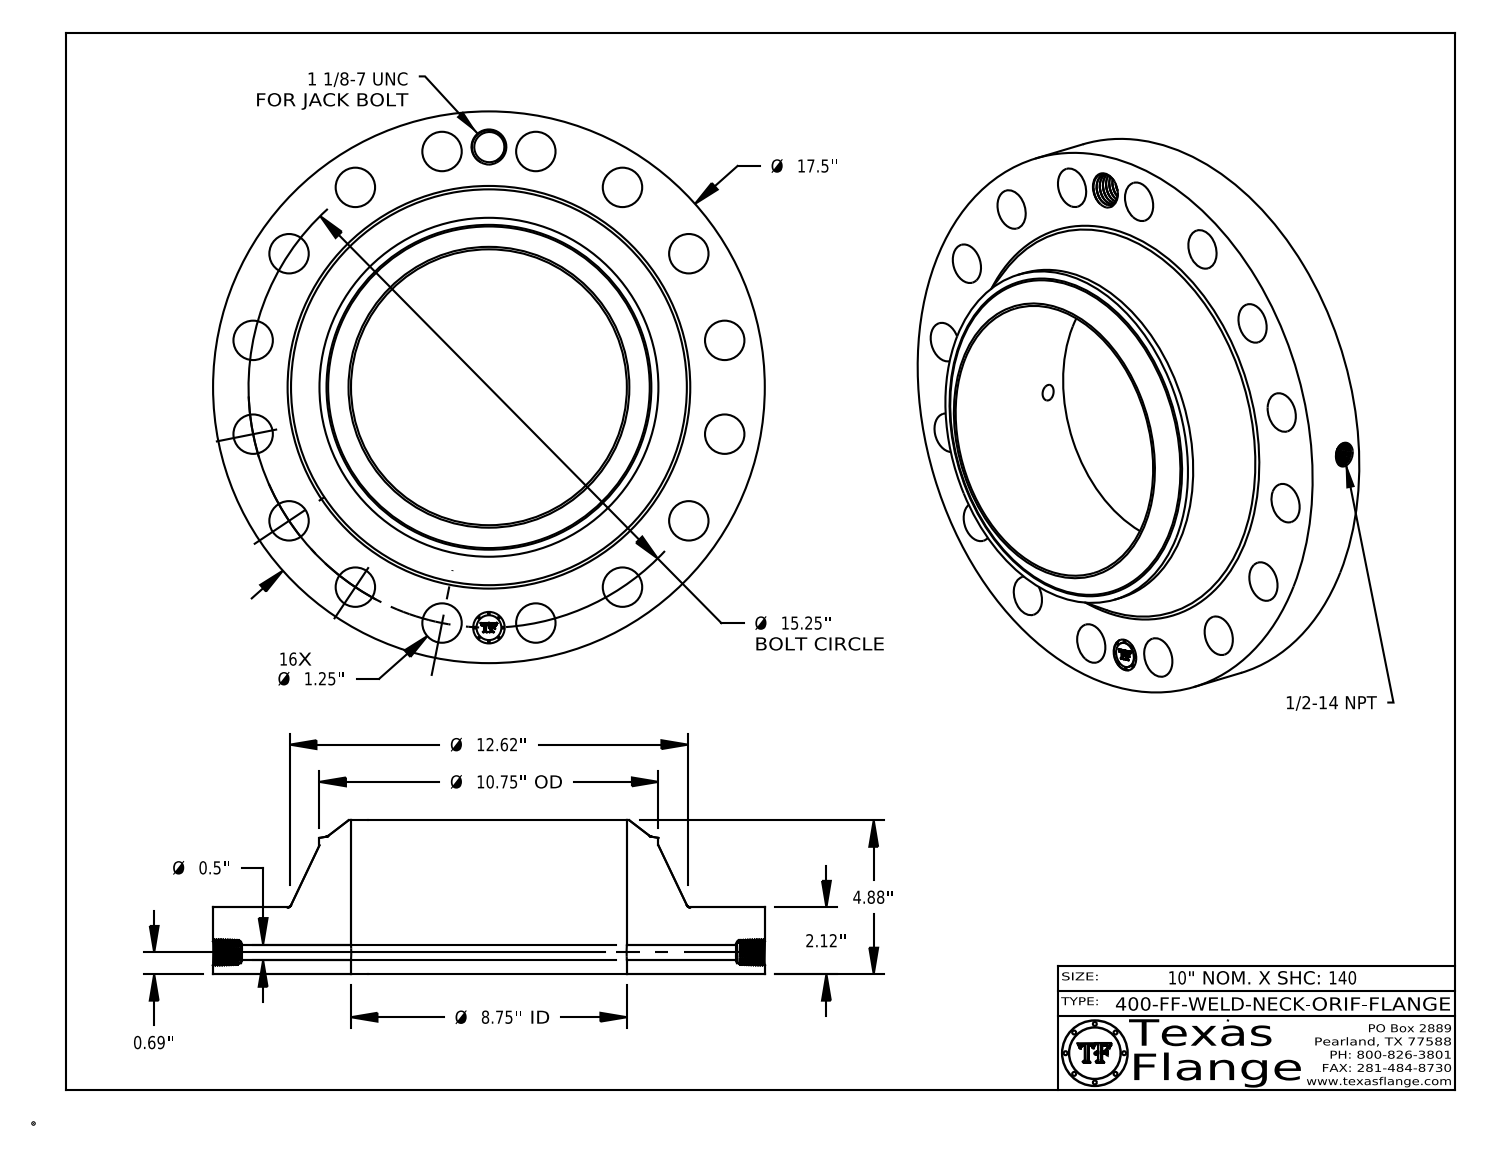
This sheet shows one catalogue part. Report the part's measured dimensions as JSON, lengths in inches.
{"part_name": "400-FF-WELD-NECK", "step_written_by": "CATIA V5 STEP AP214 (AUTOMOTIVE_DESIGN)", "units": "inches", "bodies": {"solids": 1, "faces": 786, "planar": 368, "cylindrical": 107, "other": 311}, "overall_size": [17.5, 17.5, 4.88], "volume_in3": 444.5, "surface_area_in2": 789, "round_holes": [[1.25, 16], [0.5, 1], [0.672, 1], [0.984, 1], [1, 1], [8.75, 1]], "round_bosses_or_shafts": [[0.061, 8], [17.5, 1], [10.75, 1], [0.788, 1]], "face_to_face_distances": [2.12, 4.88, 2.76, 0.015, 2.105, 2.775, 0.298, 0.292, 0.054, 0.248], "hole_center_spacings": [5.836, 7.625, 10.783, 14.089, 14.957, 2.975, 2.975, 8.472]}
